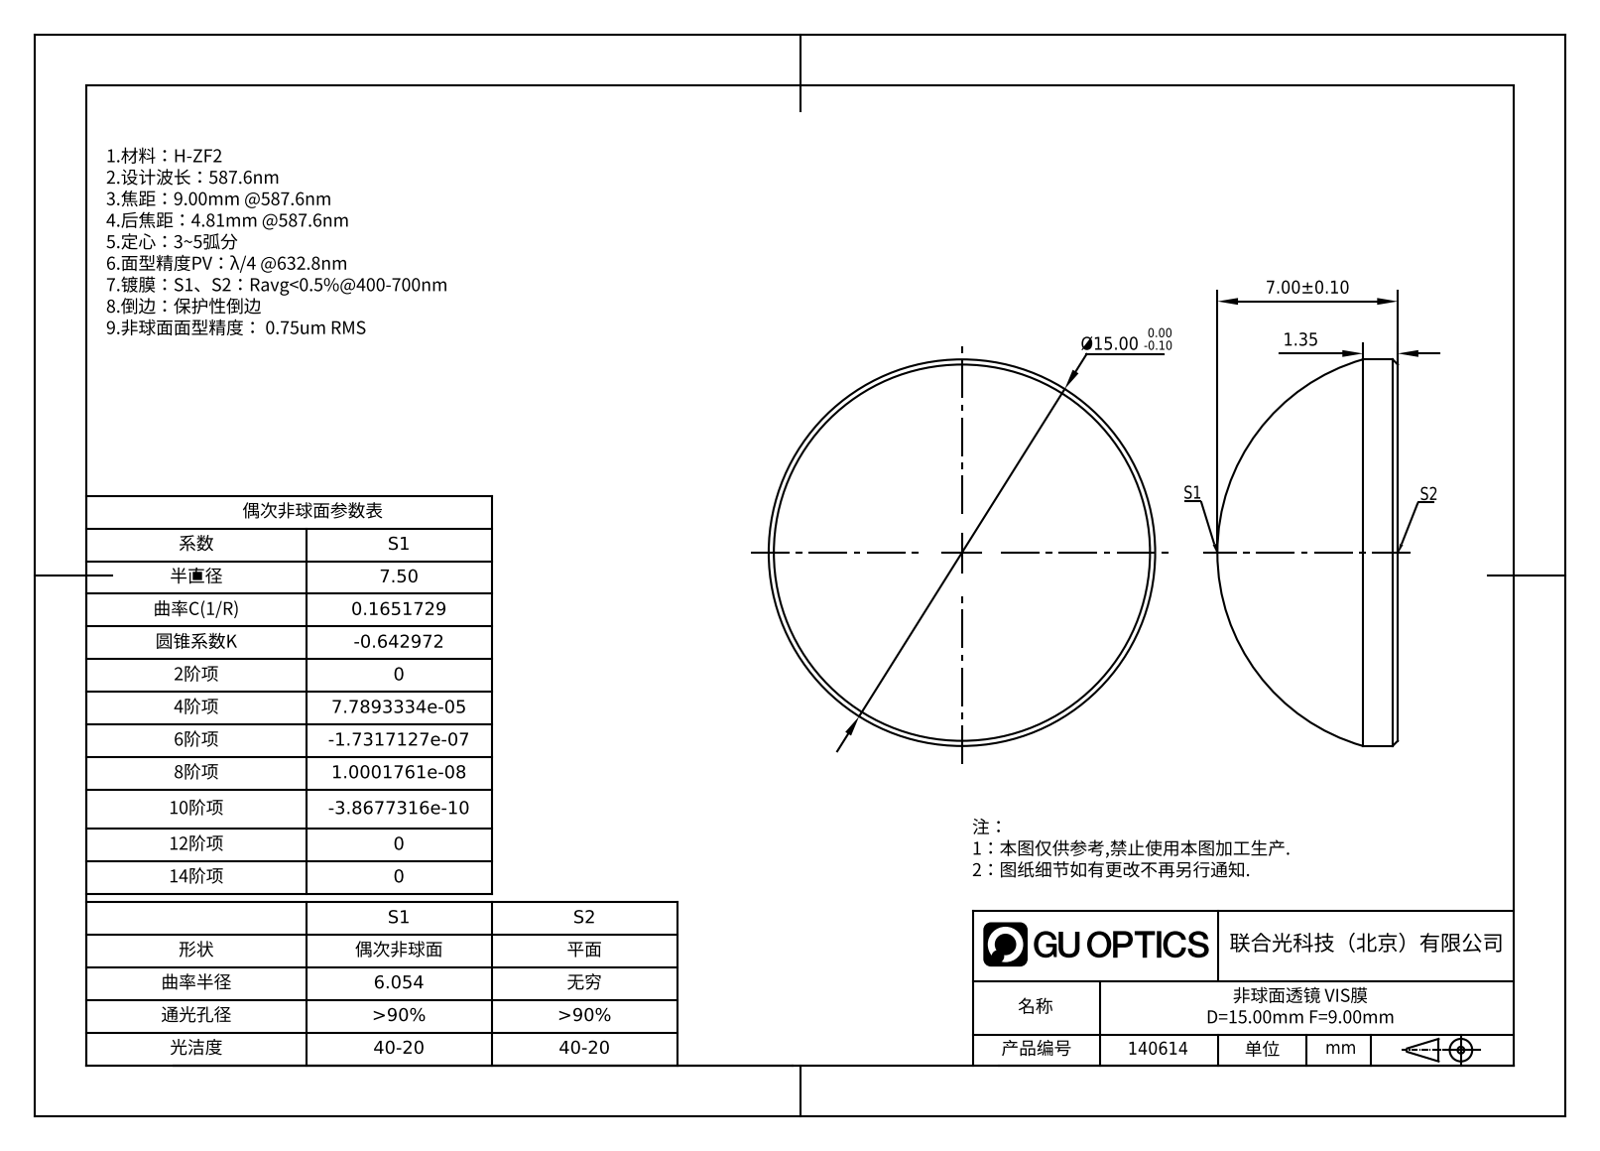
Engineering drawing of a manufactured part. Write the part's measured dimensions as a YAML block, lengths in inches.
part_name: "GLA11-015-9-VIS"
step_written_by: "SolidWorks 2022 (AUTOMOTIVE_DESIGN)"
units: inches
bodies: {solids: 1, faces: 7, planar: 1, cylindrical: 2, other: 4}
overall_size: [0.591, 0.591, 0.276]
volume: 0.051
surface_area: 0.794
round_bosses_or_shafts:
  - {diameter: 0.591, count: 1}
